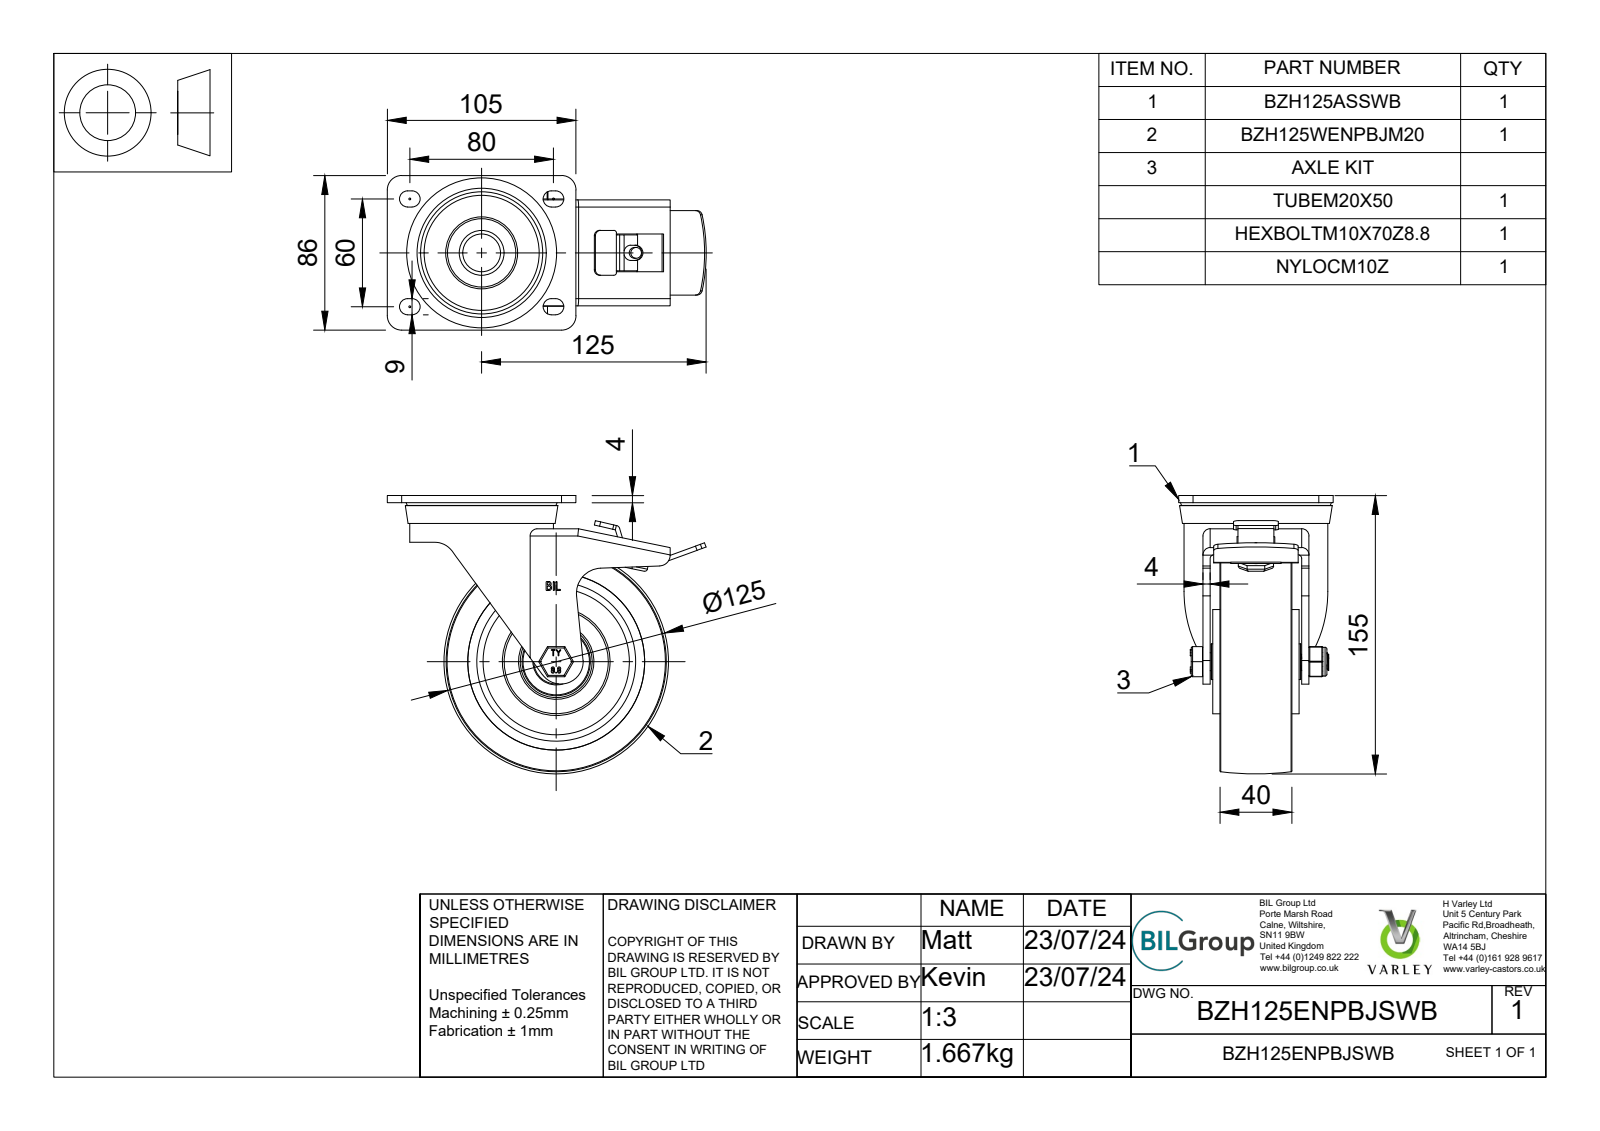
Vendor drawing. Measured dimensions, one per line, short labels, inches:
name: BZH125ENPBJSWB v4; BZH125ASSWB v1; ZINC PLATED, PRESSED STEEL TOP PLATE; ZINC PLATED, PRESSED STEEL FORKS (+8 more)
written by: Autodesk Translation Framework v13.14.0.145 (AUTOMOTIVE_DESIGN)
unit: in
bodies: 41 solids, 1464 faces (656 planar, 284 cylindrical, 524 other)
size: 6.988 × 6.102 × 3.386
volume: 31.79 in³; area: 326.2 in²
holes: 2× ⌀0.984, 1× ⌀0.236, 1× ⌀0.394, 1× ⌀0.402, 1× ⌀0.413, 1× ⌀0.472, 1× ⌀0.787, 1× ⌀1.024, 1× ⌀1.26, 1× ⌀1.378, 1× ⌀1.417, 1× ⌀1.496
bosses: 18× ⌀0.315, 1× ⌀3.15, 1× ⌀2.441, 1× ⌀2.362, 1× ⌀2.283, 1× ⌀1.457, 1× ⌀1.22, 1× ⌀1.063
rounds: 19× R0.02, 14× R0.03, 8× R0.059, 8× R0.079, 8× R0.177, 6× R0.118, 4× R0.157, 4× R0.315
face distances: 0.157, 0.217, 1.949, 0.374, 0.886, 1.575, 0.906, 2.165, 1.791, 0.295
